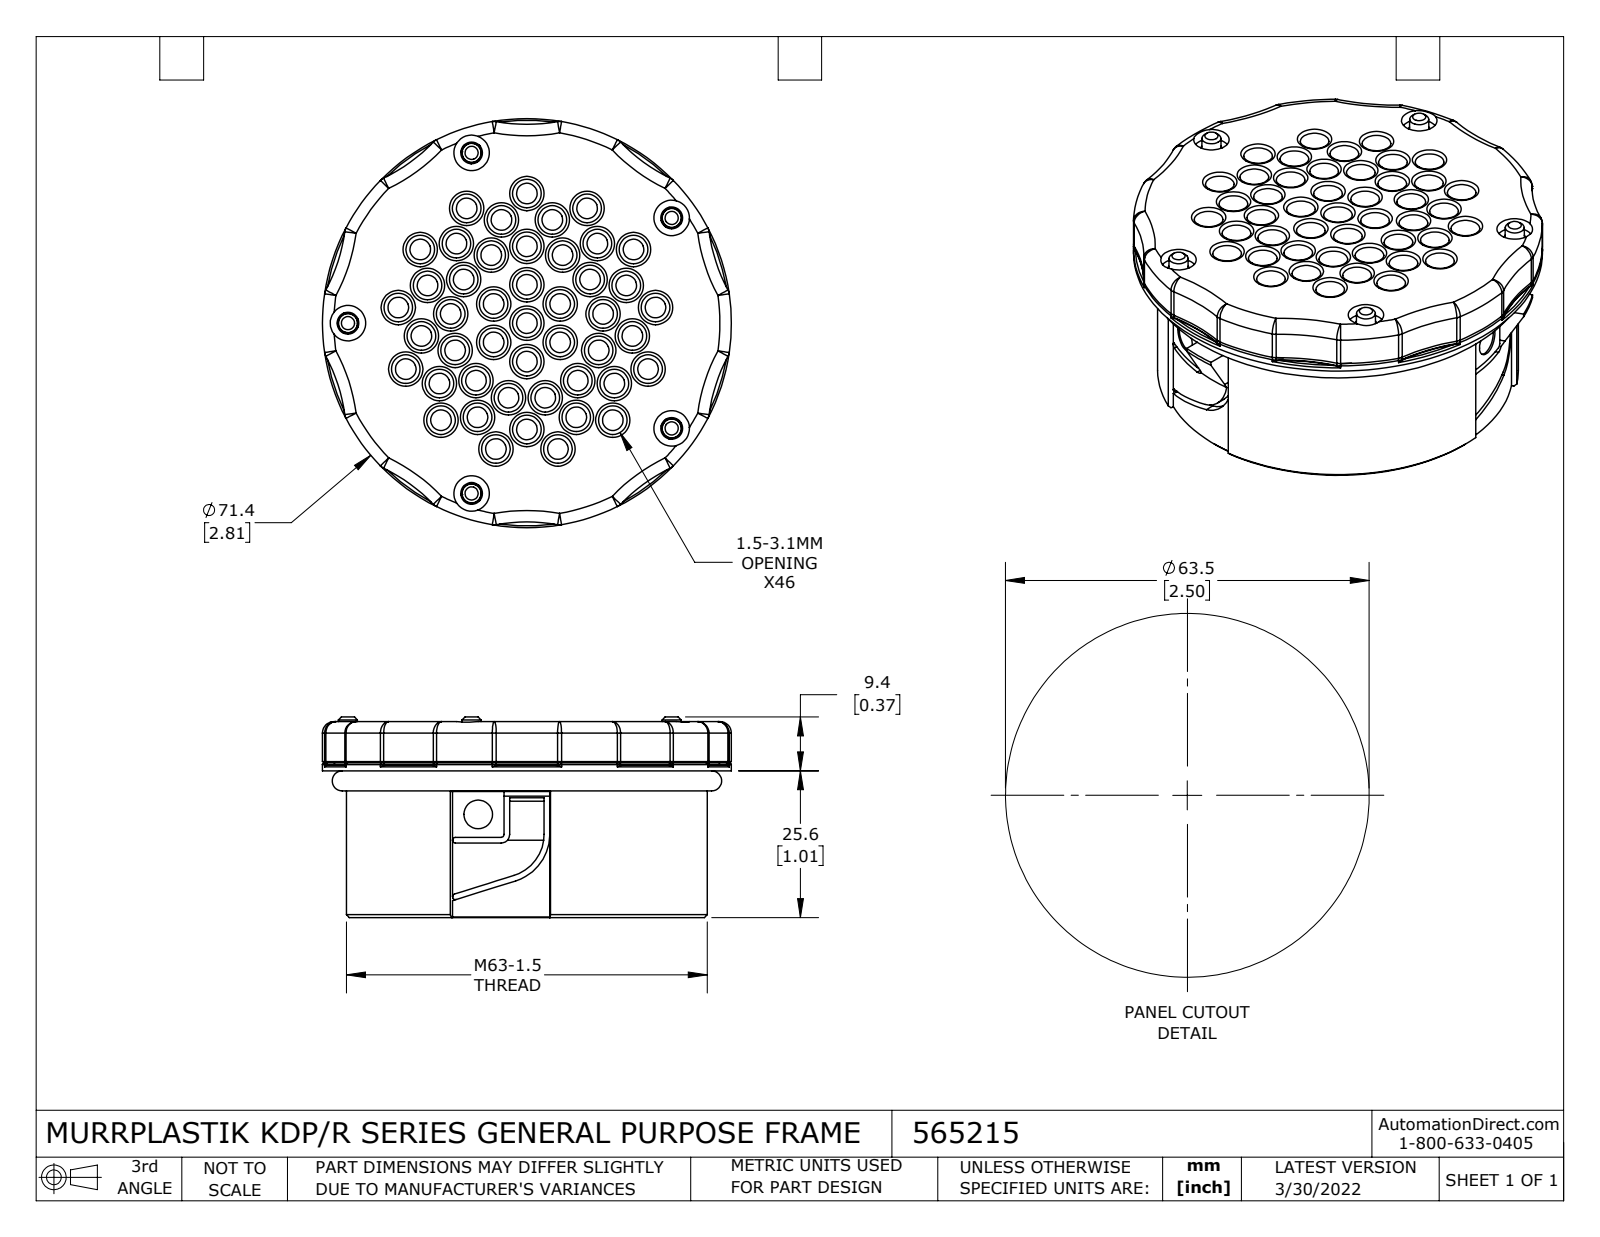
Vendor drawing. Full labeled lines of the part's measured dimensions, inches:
Part name (STEP PRODUCT): 565215
STEP written by: SolidWorks 2021 (CONFIG_CONTROL_DESIGN)
Units: inches
Bodies: 6 solids, 977 faces (97 planar, 484 cylindrical, 396 other)
Overall size (bounding box): 2.811 × 2.811 × 1.378
Volume: 2.741 in³ · Surface area: 74.77 in²
Round holes (diameter × count): ⌀0.197 ×49, ⌀0.142 ×46, ⌀0.217 ×46, ⌀0.15 ×8, ⌀0.244 ×5, ⌀0.157 ×3, ⌀2.161 ×1, ⌀2.283 ×1, ⌀2.654 ×1
Round bosses / shafts (diameter × count): ⌀0.189 ×3, ⌀2.811 ×1, ⌀2.614 ×1, ⌀2.52 ×1, ⌀2.48 ×1, ⌀2.429 ×1, ⌀2.323 ×1, ⌀2.193 ×1
Partial cylindrical surfaces — rounded edges, fillets, slot ends (radius × count): R0.079 ×20, R1.181 ×10, R0.02 ×9, R0.012 ×6, R0.059 ×3, R0.295 ×3, R0.335 ×3, R0.098 ×2
Main face-to-face distances: 0.069, 0.138, 0.157, 0.295, 0.226, 0.185, 0.323, 0.063, 0.043, 0.254
Hole centre spacings: 0.252, 1.437, 0.93, 1.769, 0.594, 1.218, 1.333, 1.666
